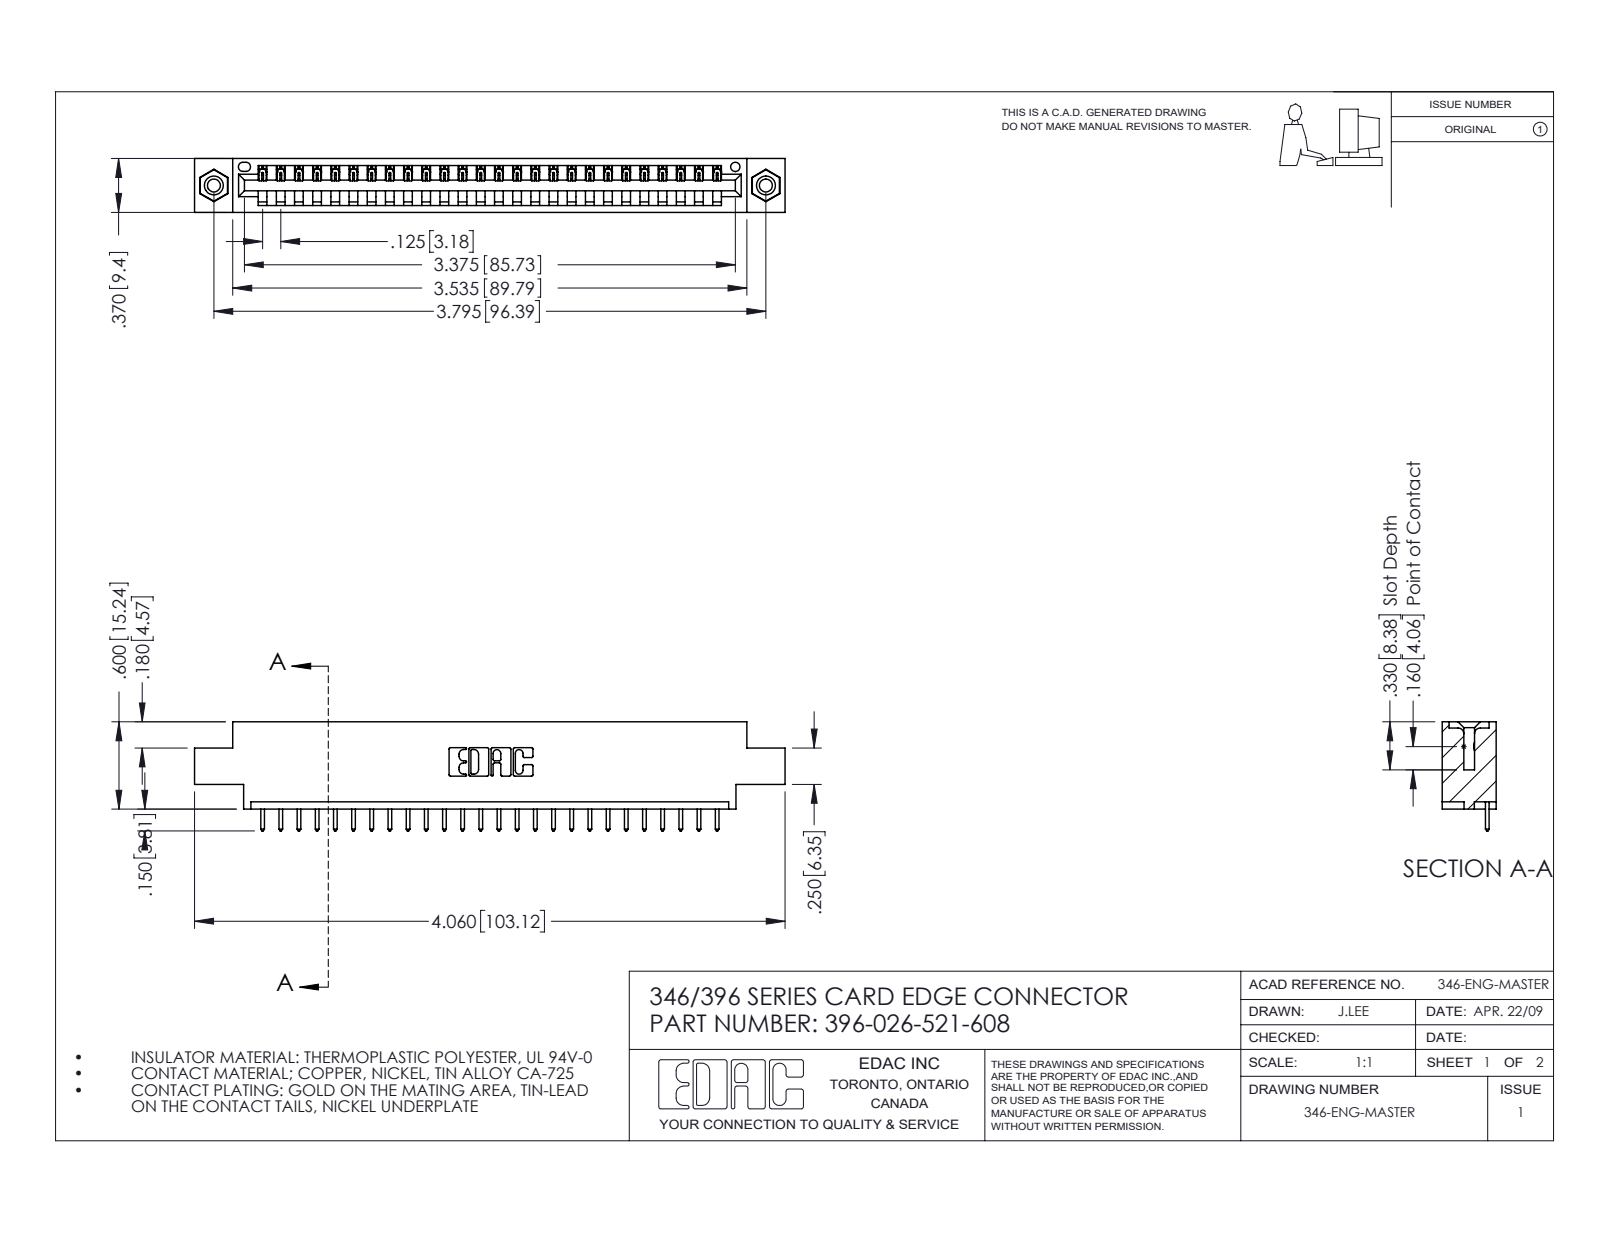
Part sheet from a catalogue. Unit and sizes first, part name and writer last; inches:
Units: inches
Overall size (bounding box): 4.06 × 0.75 × 0.37
Round holes (diameter × count): ⌀0.089 ×2, ⌀0.125 ×2, ⌀0.156 ×2, ⌀0.064 ×1
Round bosses / shafts (diameter × count): ⌀0.155 ×2
Partial cylindrical surfaces — rounded edges, fillets, slot ends (radius × count): R0.006 ×52, R0.01 ×52, R0.01 ×22, R0.007 ×6, R0.031 ×6, R0.026 ×3, R0.031 ×2, R0.04 ×2
Main face-to-face distances: 0.048, 0.322, 0.37, 0.25, 0.072, 0.298, 0.025, 0.222, 0.148, 0.1
Hole centre spacings: 0.246, 3.587, 3.795
Volume: 0.581 in³ · Surface area: 18.01 in²
Bodies: 29 solids, 1694 faces (1152 planar, 526 cylindrical, 16 other)
Part name (STEP PRODUCT): 396-026-521-608; 345-250-001_345-250-003-102; 345-292-001_345-293-121; 346 Part_0.170 Offset - 0.156 Dia-TI
STEP written by: SolidWorks 2016 (CONFIG_CONTROL_DESIGN)
